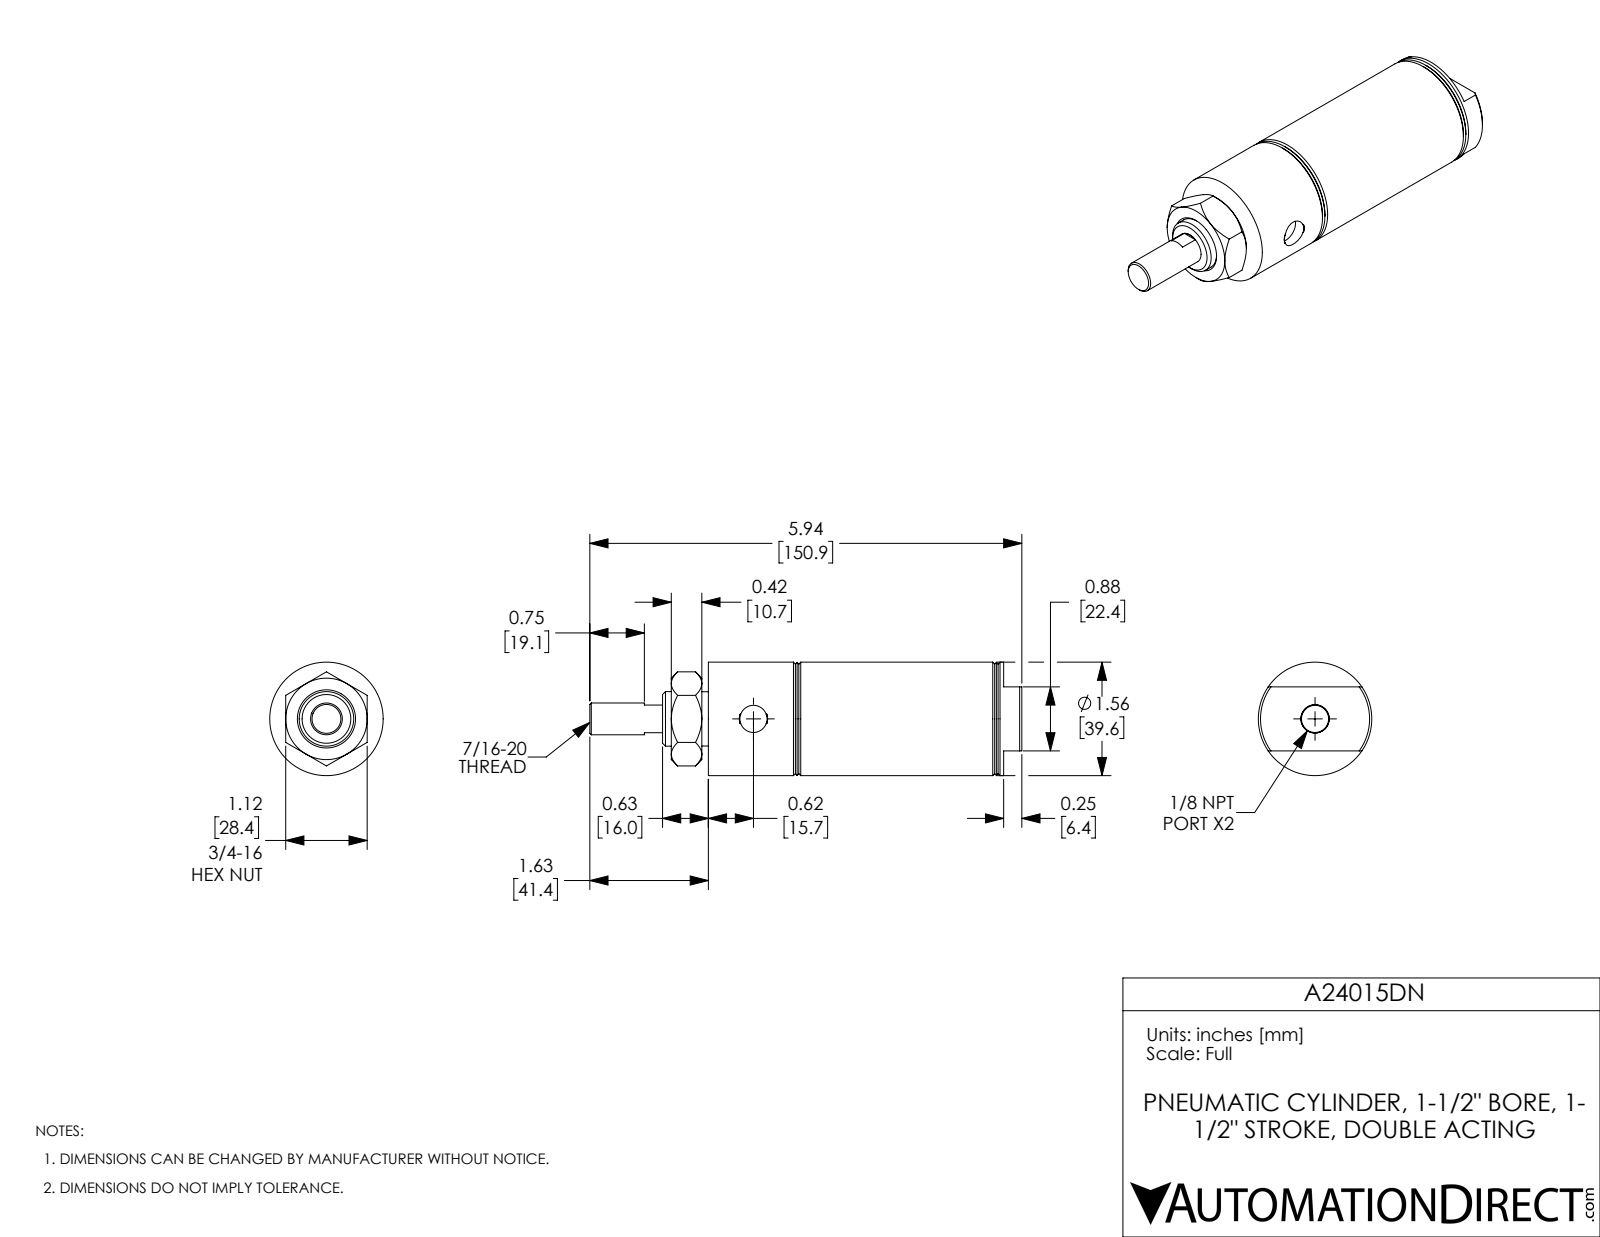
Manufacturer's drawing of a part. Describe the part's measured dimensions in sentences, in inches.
The part is named "A24015DN_Mounting Nut_D-3556; A24015DN; A24015DN-MainBody; A24015DN-Rod". Its 3-D file was written by "SolidWorks 2017 (AUTOMOTIVE_DESIGN)". It is 3 solids with 104 faces: 32 planar, 24 cylindrical and 48 other. Overall it measures 5.94 by 1.56 by 1.56 inches. Its volume is 6.289 cubic inches and its surface area 58.11 square inches. Round holes: 2 of diameter 0.374, 1 of diameter 0.437, 1 of diameter 0.75, 1 of diameter 1.5. Round bosses or shafts: 1 of diameter 1.56, 1 of diameter 0.746. The main face-to-face distances are 0.5, 2, 1.5, 3.34, 2.84, 1.34, 2.97, 0.97, 1.47, 4.31.
